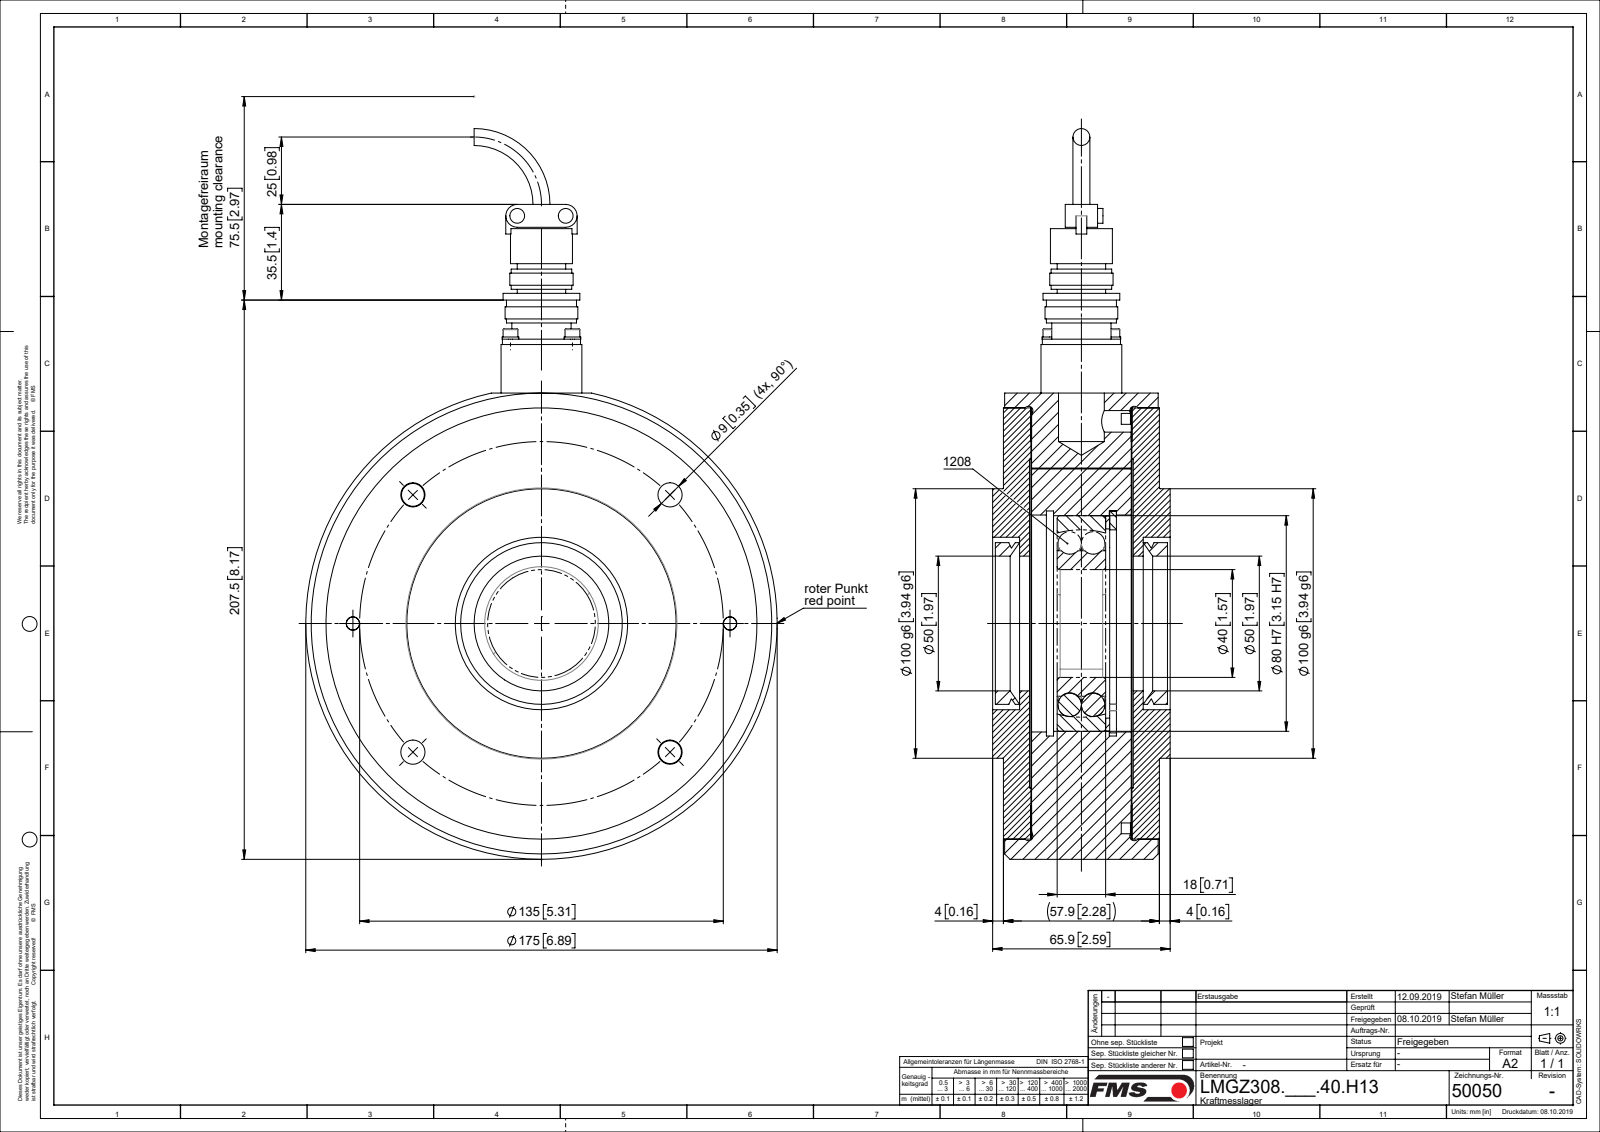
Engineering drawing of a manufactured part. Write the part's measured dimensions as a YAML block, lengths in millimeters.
part_name: "L50050; L4857104; ~TEIL1; L49026 (+8 more)"
step_written_by: "Mechanical Desktop 2007 (CONFIG_CONTROL_DESIGN)"
units: millimeters
bodies: {solids: 23, faces: 409, planar: 106, cylindrical: 243, other: 60}
overall_size: [271.15, 175, 65.9]
volume: 1270000
surface_area: 276472
round_holes:
  - {diameter: 2.6, count: 4}
  - {diameter: 3.2, count: 4}
  - {diameter: 3.4, count: 4}
  - {diameter: 9, count: 4}
  - {diameter: 5.15, count: 2}
  - {diameter: 6.6, count: 2}
  - {diameter: 11, count: 2}
  - {diameter: 23, count: 1}
  - {diameter: 40, count: 1}
  - {diameter: 48, count: 1}
  - {diameter: 50, count: 1}
  - {diameter: 62.1, count: 1}
round_bosses_or_shafts:
  - {diameter: 5.5, count: 6}
  - {diameter: 6.2, count: 4}
  - {diameter: 3, count: 4}
  - {diameter: 2.5, count: 4}
  - {diameter: 10, count: 2}
  - {diameter: 6, count: 2}
  - {diameter: 175, count: 1}
  - {diameter: 160, count: 1}
partial_cylinders:
  - {radius: 4.25, count: 2}
  - {radius: 7.5, count: 2}
face_to_face_distances: [37.25, 10.2, 10.45, 47.45, 47.7, 37, 37.5, 0.5, 38, 9.7]
hole_center_spacings: [16.26, 23, 52.67, 67.5, 95.46, 127.04, 32.53, 70]
